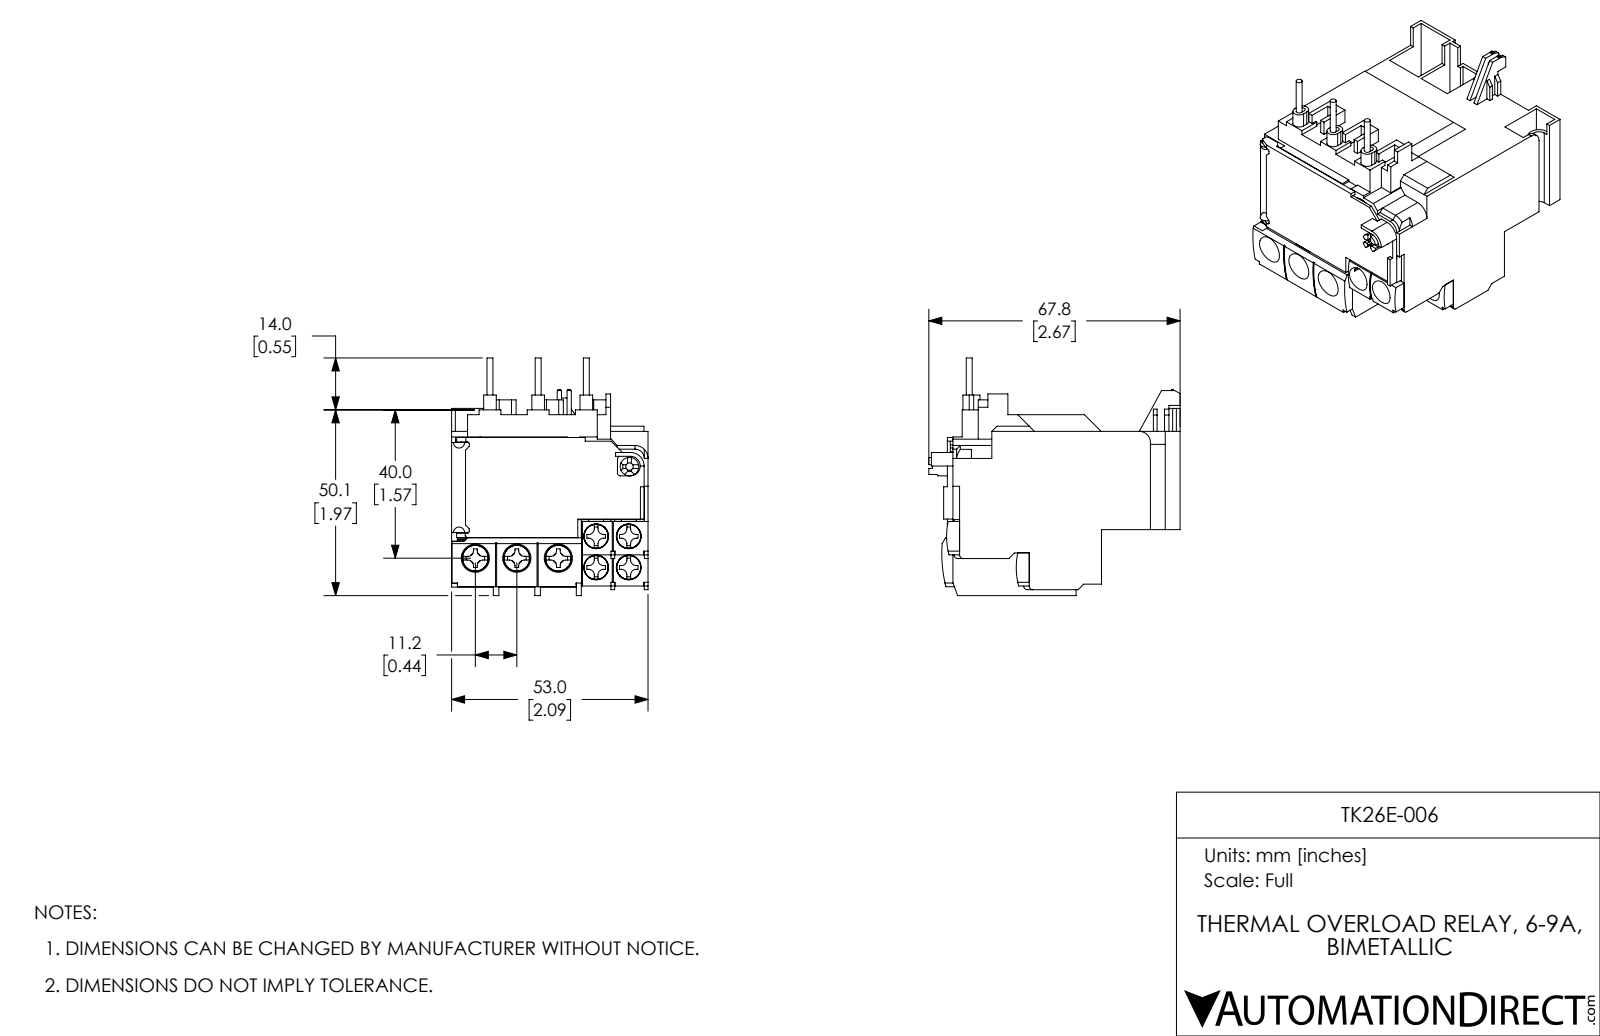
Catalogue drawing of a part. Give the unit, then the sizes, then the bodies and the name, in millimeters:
Units: millimetres
Overall size (bounding box): 67.8 × 64.1 × 53
Round holes (diameter × count): ⌀3.5 ×4, ⌀3.6 ×4, ⌀6.7 ×4, ⌀4 ×3, ⌀4.1 ×3, ⌀7.6 ×3, ⌀1 ×1, ⌀2 ×1, ⌀5 ×1, ⌀11 ×1
Round bosses / shafts (diameter × count): ⌀6.6 ×4, ⌀1.6 ×3, ⌀6 ×1
Partial cylindrical surfaces — rounded edges, fillets, slot ends (radius × count): R1.5 ×28, R1 ×8, R0.5 ×6, R1.7 ×6, R0.8 ×5, R1.2 ×4, R4.3 ×4, R4.8 ×3
Main face-to-face distances: 1, 9, 1.5, 12, 53, 2, 10, 11, 8.7, 0.7
Hole centre spacings: 8.4, 8.8, 11.2, 12.2, 9.6, 10.5, 11.8, 18.8
Volume: 99 940 mm³ · Surface area: 38 810 mm²
Bodies: 38 solids, 1480 faces (1225 planar, 220 cylindrical, 35 other)
Part name (STEP PRODUCT): TK26E-006
STEP written by: SolidWorks 2017 (AUTOMOTIVE_DESIGN)
